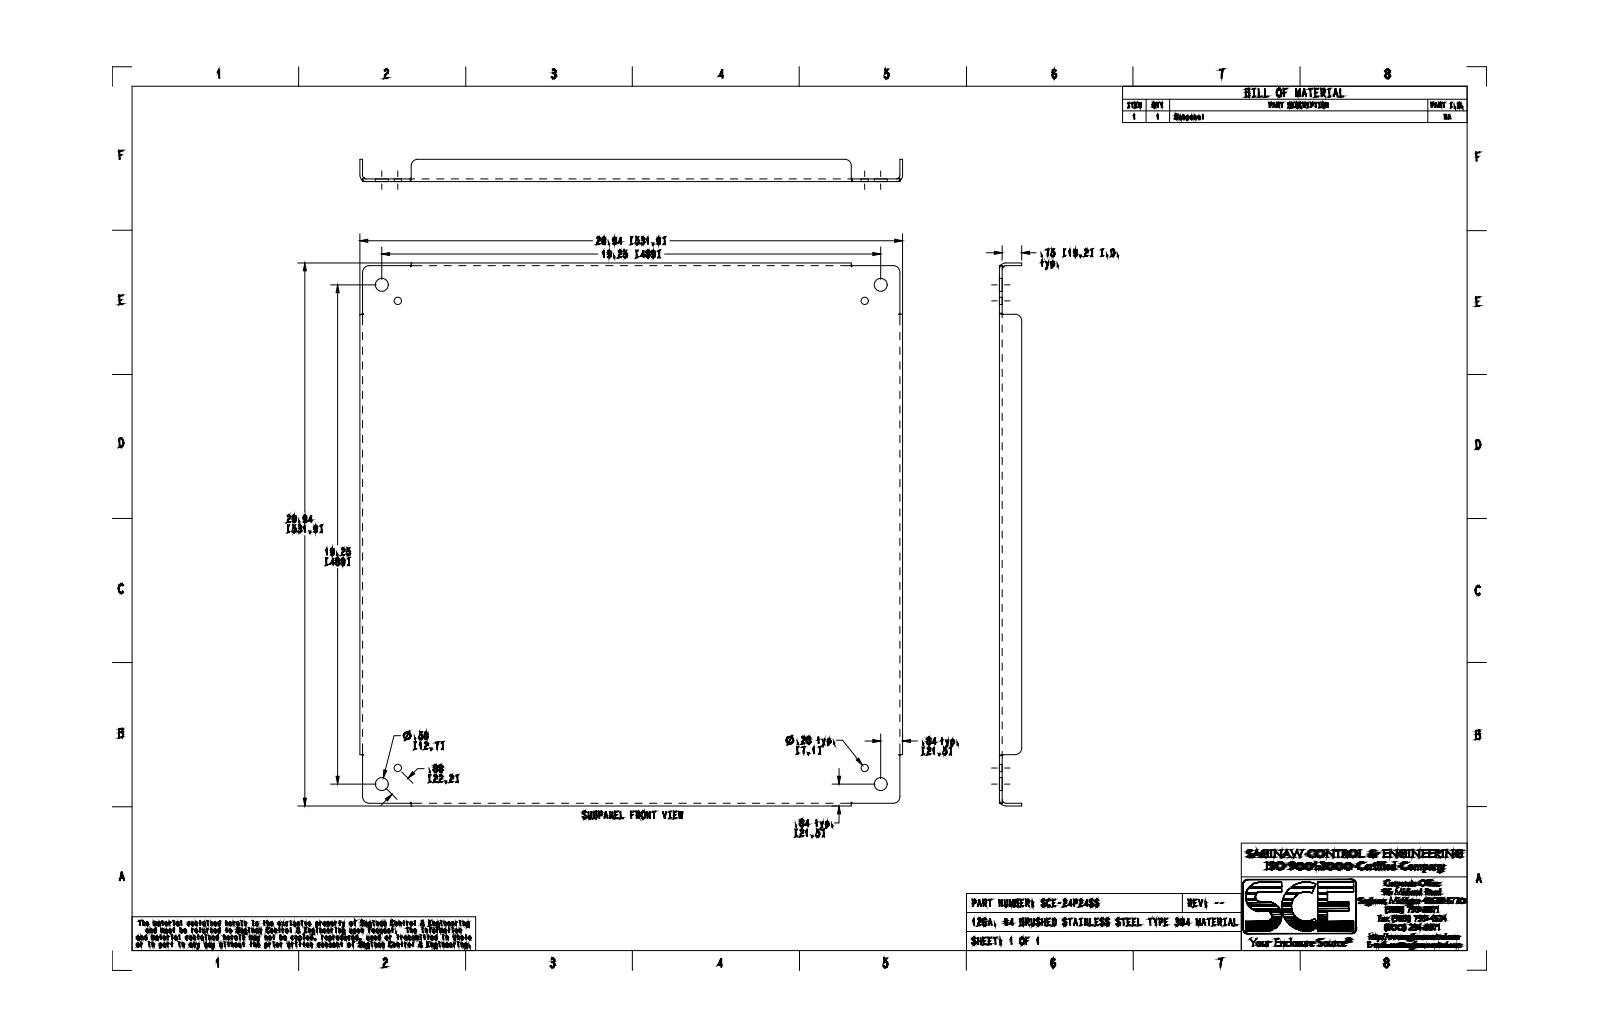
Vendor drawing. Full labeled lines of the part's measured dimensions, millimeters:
Part name (STEP PRODUCT): SCE-24P24SS
STEP written by: SolidWorks 2019 (CONFIG_CONTROL_DESIGN)
Units: millimetres
Bodies: 1 solid, 82 faces (30 planar, 28 cylindrical, 24 other)
Overall size (bounding box): 531.9 × 531.9 × 21.8
Volume: 820 300 mm³ · Surface area: 627 600 mm²
Round holes (diameter × count): ⌀7.1 ×4, ⌀12.7 ×4
Partial cylindrical surfaces — rounded edges, fillets, slot ends (radius × count): R6.4 ×8, R6.2 ×4, R3.6 ×2, R3.6 ×2
Main face-to-face distances: 2.6, 529.3, 526.6, 531.9, 19.2, 21.8, 50.3, 481.7, 47.6, 479
Hole centre spacings: 473.5, 22.2, 457.6, 489, 669.3, 647.1, 691.5
